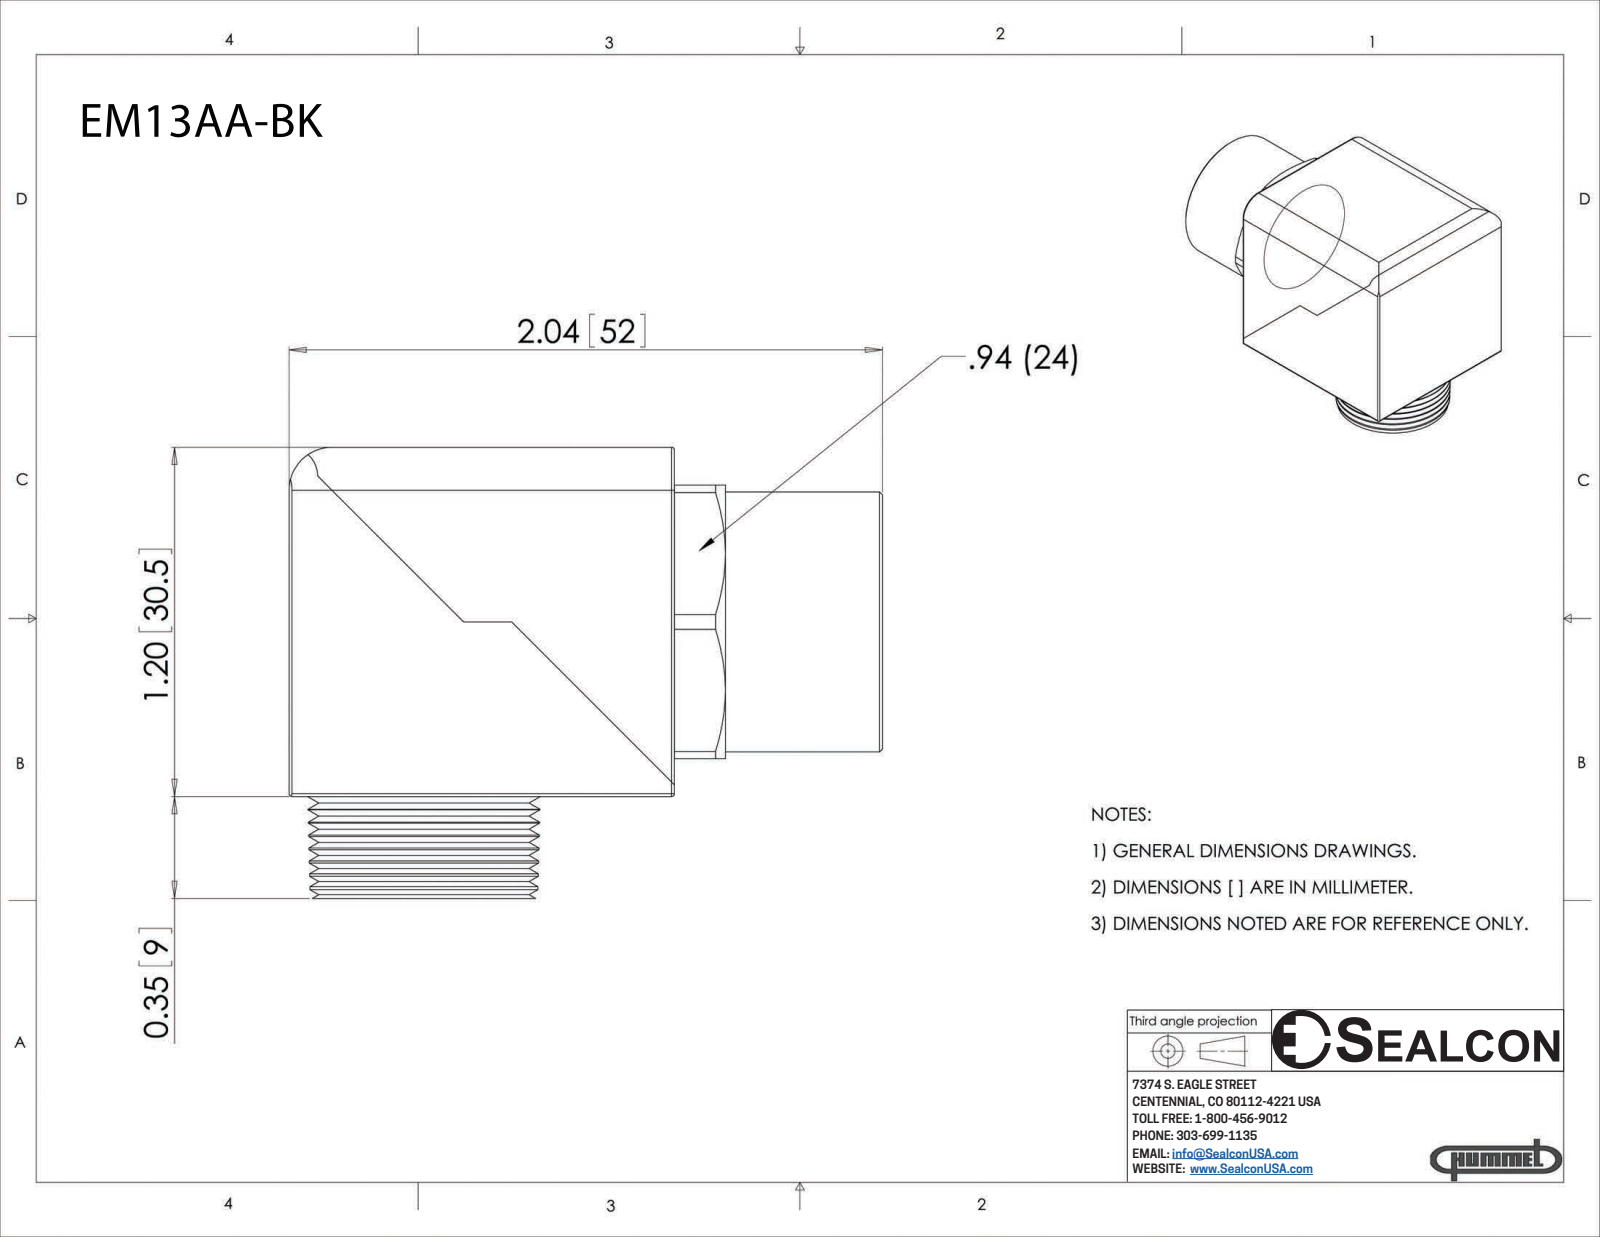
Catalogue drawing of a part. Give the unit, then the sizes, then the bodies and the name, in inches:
Units: inches
Overall size (bounding box): 2.04 × 1.55 × 1.2
Round holes (diameter × count): ⌀0.44 ×2, ⌀0.8 ×1
Round bosses / shafts (diameter × count): ⌀0.893 ×1
Partial cylindrical surfaces — rounded edges, fillets, slot ends (radius × count): R0.01 ×7, R0.147 ×3, R0.098 ×1, R0.529 ×1
Main face-to-face distances: 1.2, 0.117, 1.325, 0.6, 0.175, 1.5, 0.35, 1.55, 0.95, 0.94
Volume: 1.941 in³ · Surface area: 20.44 in²
Bodies: 2 solids, 130 faces (31 planar, 34 cylindrical, 65 other)
Part name (STEP PRODUCT): EM13AA-BK
STEP written by: SolidWorks 2007 (AUTOMOTIVE_DESIGN)
